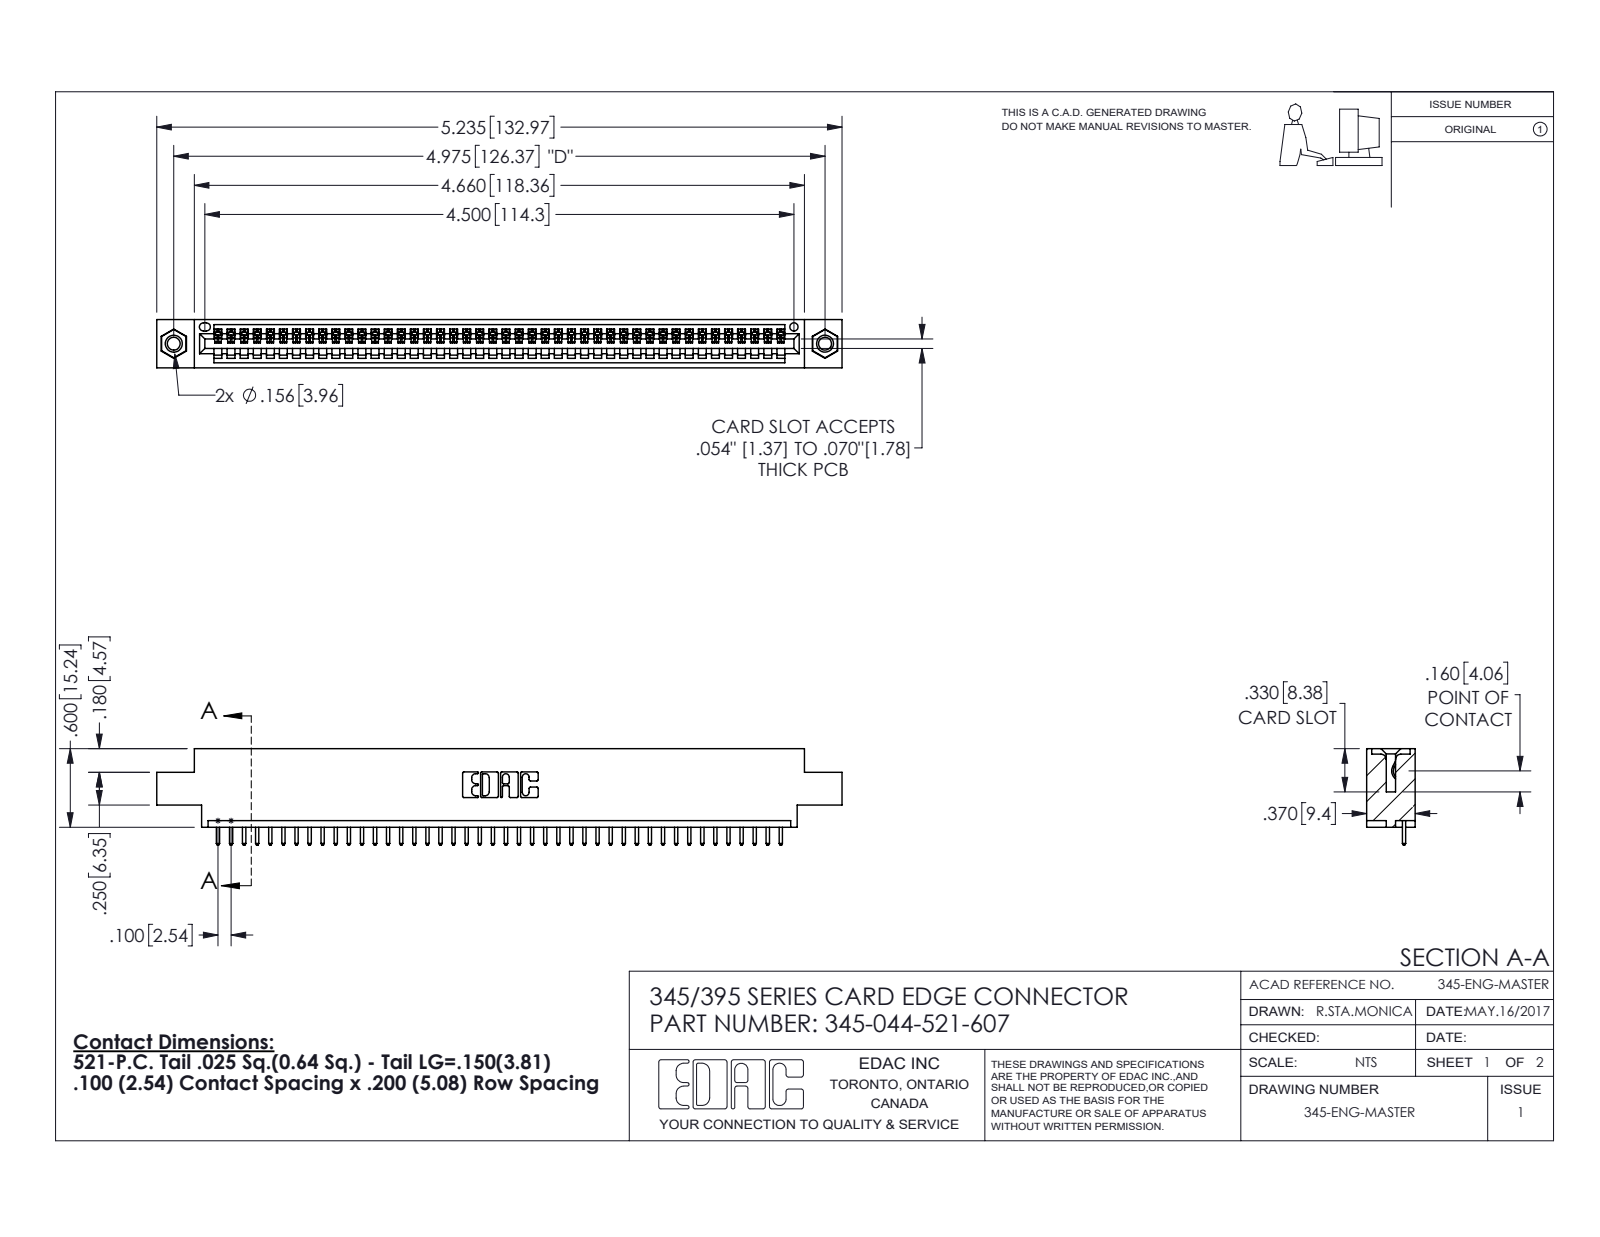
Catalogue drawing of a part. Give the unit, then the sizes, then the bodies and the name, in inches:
Units: inches
Overall size (bounding box): 5.235 × 0.737 × 0.37
Round holes (diameter × count): ⌀0.098 ×2, ⌀0.125 ×2, ⌀0.156 ×2, ⌀0.064 ×1
Round bosses / shafts (diameter × count): ⌀0.155 ×2
Partial cylindrical surfaces — rounded edges, fillets, slot ends (radius × count): R0.006 ×88, R0.01 ×88, R0.01 ×22, R0.007 ×6, R0.031 ×6, R0.026 ×3, R0.031 ×2, R0.04 ×2
Main face-to-face distances: 0.072, 0.298, 0.37, 0.2, 0.098, 0.272, 0.025, 0.225, 0.175, 0.149
Hole centre spacings: 0.27, 4.739, 4.975
Volume: 0.756 in³ · Surface area: 25.06 in²
Bodies: 47 solids, 2742 faces (1876 planar, 850 cylindrical, 16 other)
Part name (STEP PRODUCT): 345-044-521-607; 345-250-001_345-250-005-103; 345 Part_0.170 Offset - 0.156 Dia-TI; 345-292-001_345-293-121
STEP written by: SolidWorks 2016 (CONFIG_CONTROL_DESIGN)
